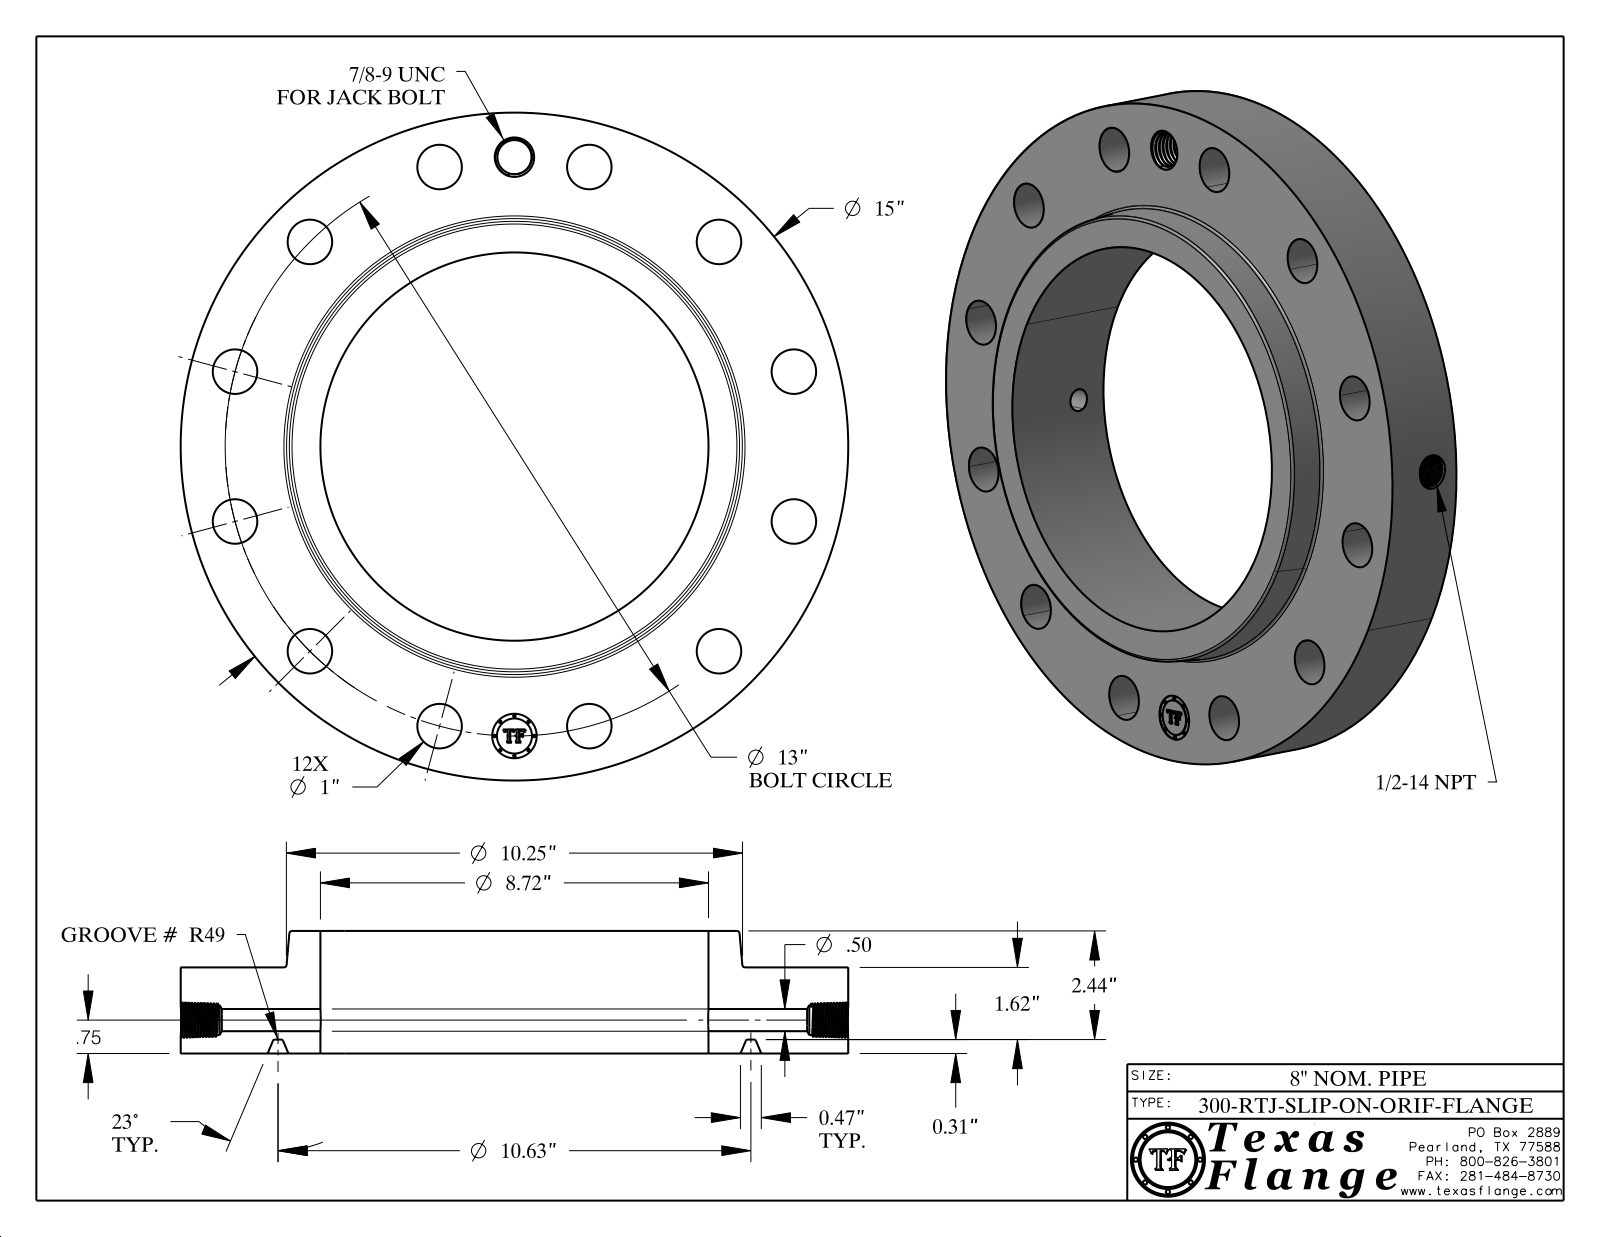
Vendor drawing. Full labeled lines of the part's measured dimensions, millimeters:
Part name (STEP PRODUCT): 300-RTJ-SLIP-ON
STEP written by: CATIA V5 STEP AP214 (AUTOMOTIVE_DESIGN)
Units: millimetres
Bodies: 1 solid, 794 faces (370 planar, 102 cylindrical, 322 other)
Overall size (bounding box): 381 × 381 × 69.9
Volume: 3 597 000 mm³ · Surface area: 329 000 mm²
Round holes (diameter × count): ⌀25.4 ×13, ⌀12.7 ×1, ⌀17.1 ×1, ⌀19.5 ×1, ⌀221.5 ×1
Round bosses / shafts (diameter × count): ⌀1.5 ×8, ⌀381 ×1, ⌀20 ×1
Main face-to-face distances: 49.1, 69.9, 20.8, 8, 41.1, 62, 48.7, 40.8, 0.4, 21.2
Hole centre spacings: 165.1, 85.5, 233.5, 286, 318.9, 330.2, 43.1, 126.4
